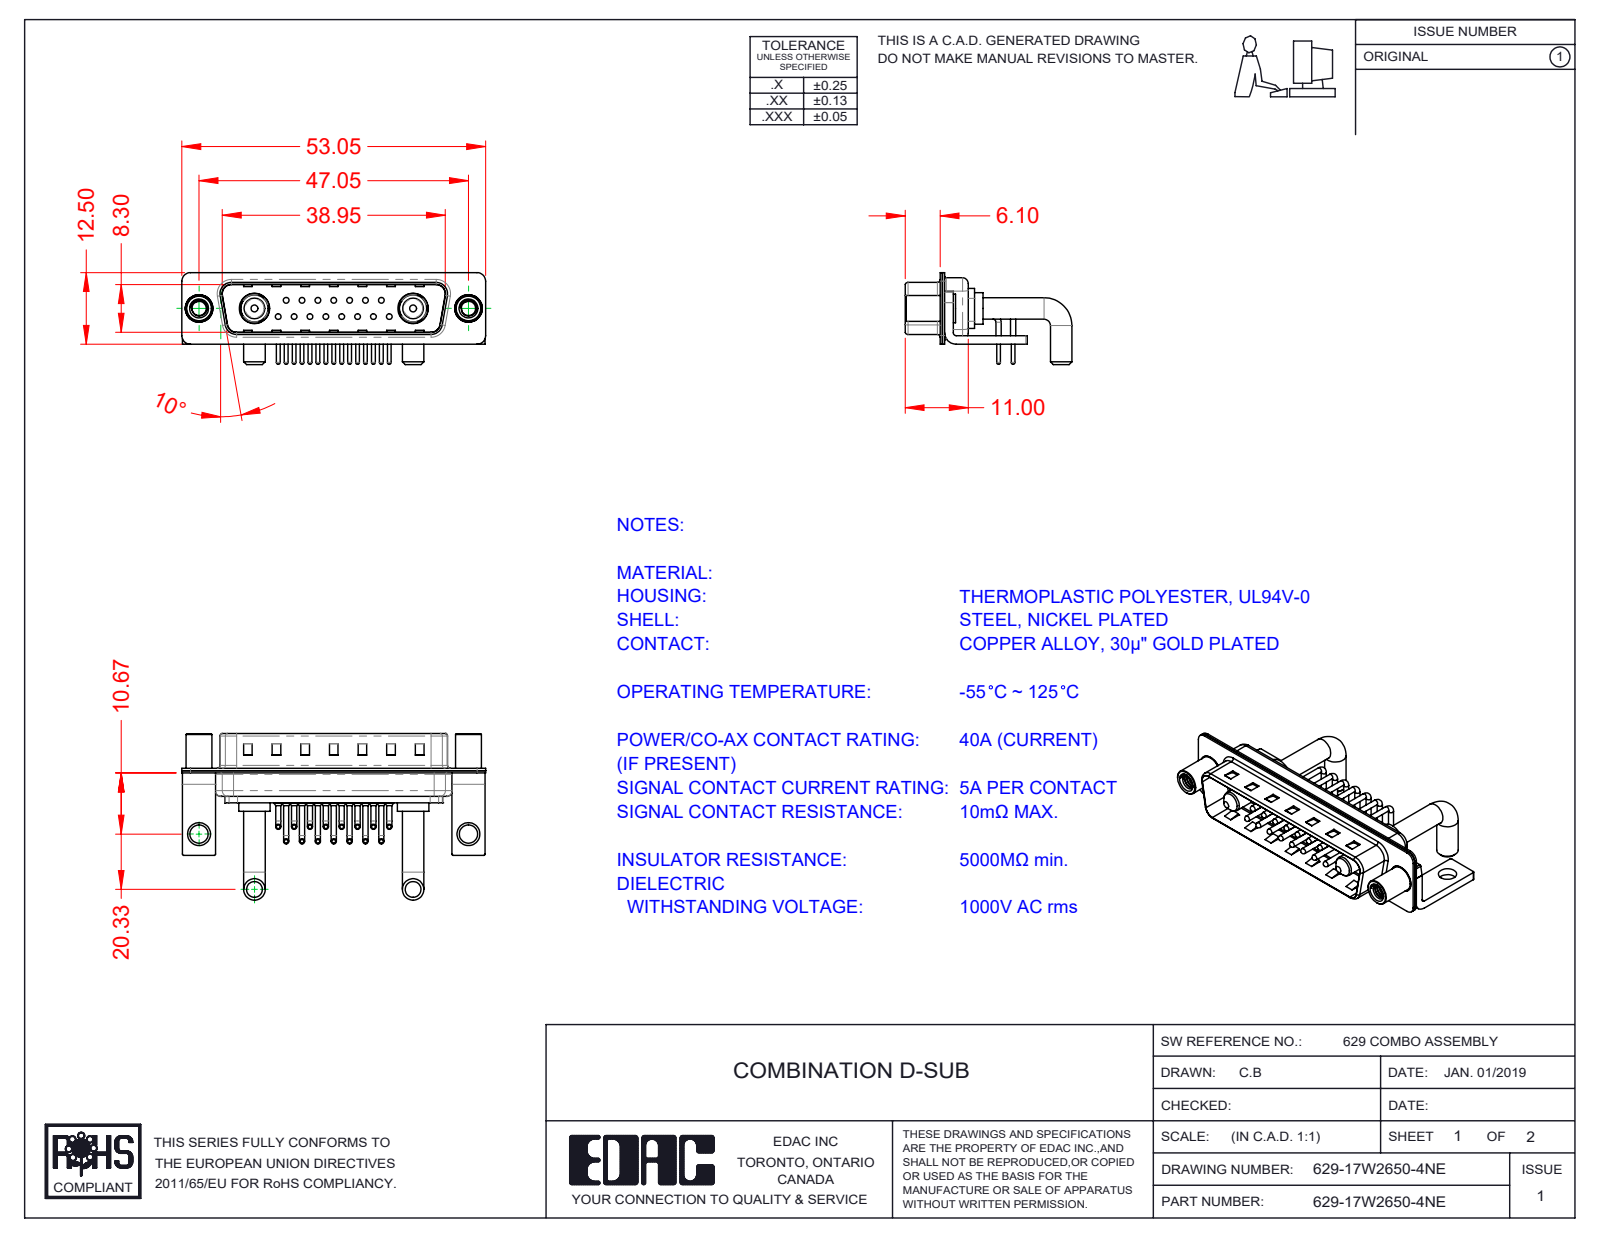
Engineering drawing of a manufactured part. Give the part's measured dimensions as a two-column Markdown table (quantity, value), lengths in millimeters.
| quantity | value |
| --- | --- |
| part name | 629Combo Shell Front_25 Contacts; 629-17W2650-4NE; 629Combo Contact Row 2; Power Pin_Ext 40A RA (+5 more) |
| STEP written by | SolidWorks 2020 (CONFIG_CONTROL_DESIGN) |
| units | millimeters |
| bodies | 26 solids, 2210 faces (1173 planar, 791 cylindrical, 246 other) |
| overall size | 53.05 × 29.11 × 16.05 |
| volume | 3 799 mm³ |
| surface area | 8 656 mm² |
| round holes (diameter × count) | 0.75 × 15, 1.6 × 15, 2 × 15, 2.5 × 2, 3.2 × 2, 4 × 2, 4.8 × 2, 4.85 × 2, 5.3 × 2 |
| round bosses / shafts (diameter × count) | 0.9 × 30, 1.5 × 15, 1 × 15, 0.65 × 15, 3.75 × 4, 5.5 × 2, 5.2 × 2, 5 × 2 |
| partial cylindrical surfaces (radius × count) | 0.25 × 16, 1.5 × 16, 1.01 × 15, 2 × 13, 0.5 × 9, 1.6 × 8, 0.6 × 4, 0.65 × 4 |
| main face-to-face distances | 0.4, 0.8, 9.5, 1.5, 9.1, 8.7, 9.9, 0.6, 0.75, 5.2 |
| hole center spacings | 3.16, 2.77, 5.54, 8.31, 5.04, 7.49, 11.08, 5.03 |
